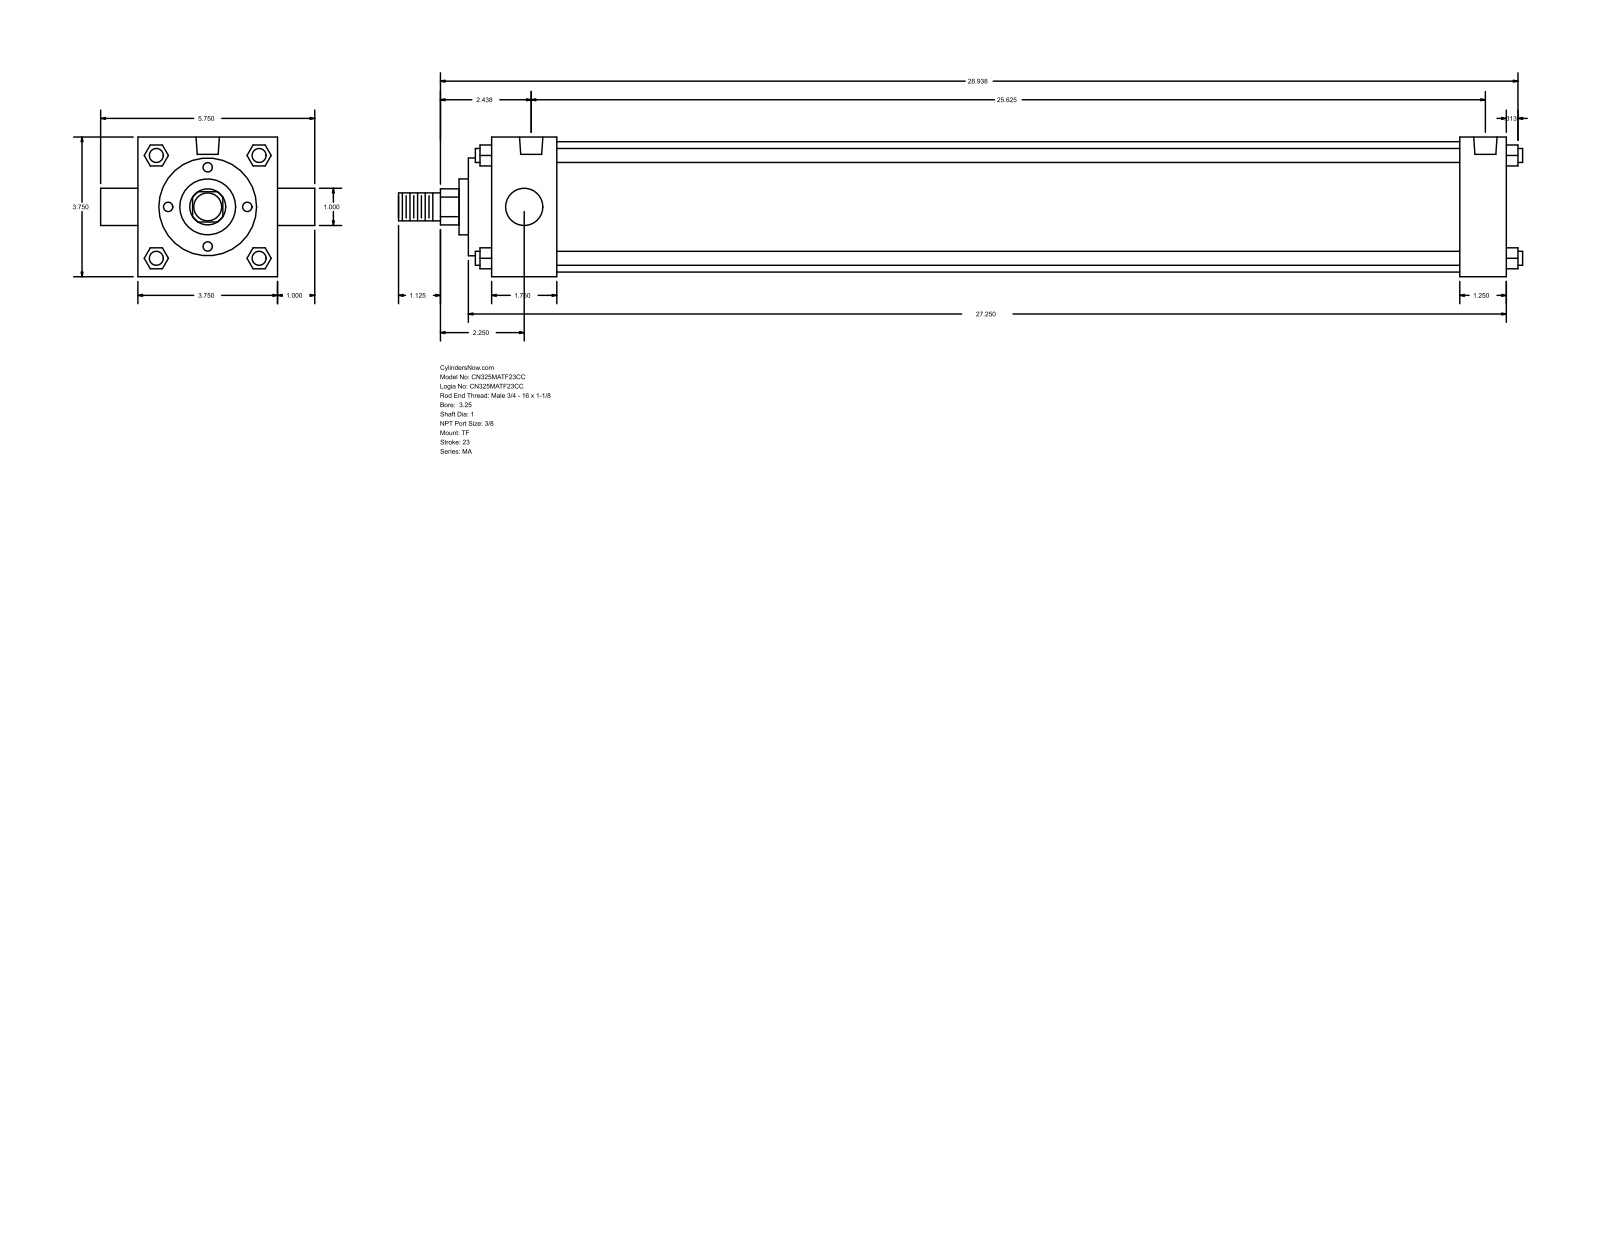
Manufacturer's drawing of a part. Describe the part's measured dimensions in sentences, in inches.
The part is named "MA_TF__0325_1". Its 3-D file was written by "GSSL Pune (CONFIG_CONTROL_DESIGN)". It is 0 solids with 122 faces: 93 planar, 29 cylindrical and 0 other. Overall it measures 30.187 by 5.75 by 3.75 inches. Round holes: 3 of diameter 0.437, 2 of diameter 0.627. Round bosses or shafts: 4 of diameter 0.375, 2 of diameter 1, 1 of diameter 3.5, 1 of diameter 2.625, 1 of diameter 1.5, 1 of diameter 0.75. Partial cylindrical surfaces (rounded edges, fillets, slot ends): 1 of radius 0.484. The main face-to-face distances are 3.75, 27.25, 1.75, 26, 24.25, 25.5, 1.25, 0.625, 2.375, 26.625. The hole center spacings are 0.187, 0.188, 25.25, 25.437, 25.438, 25.625.
